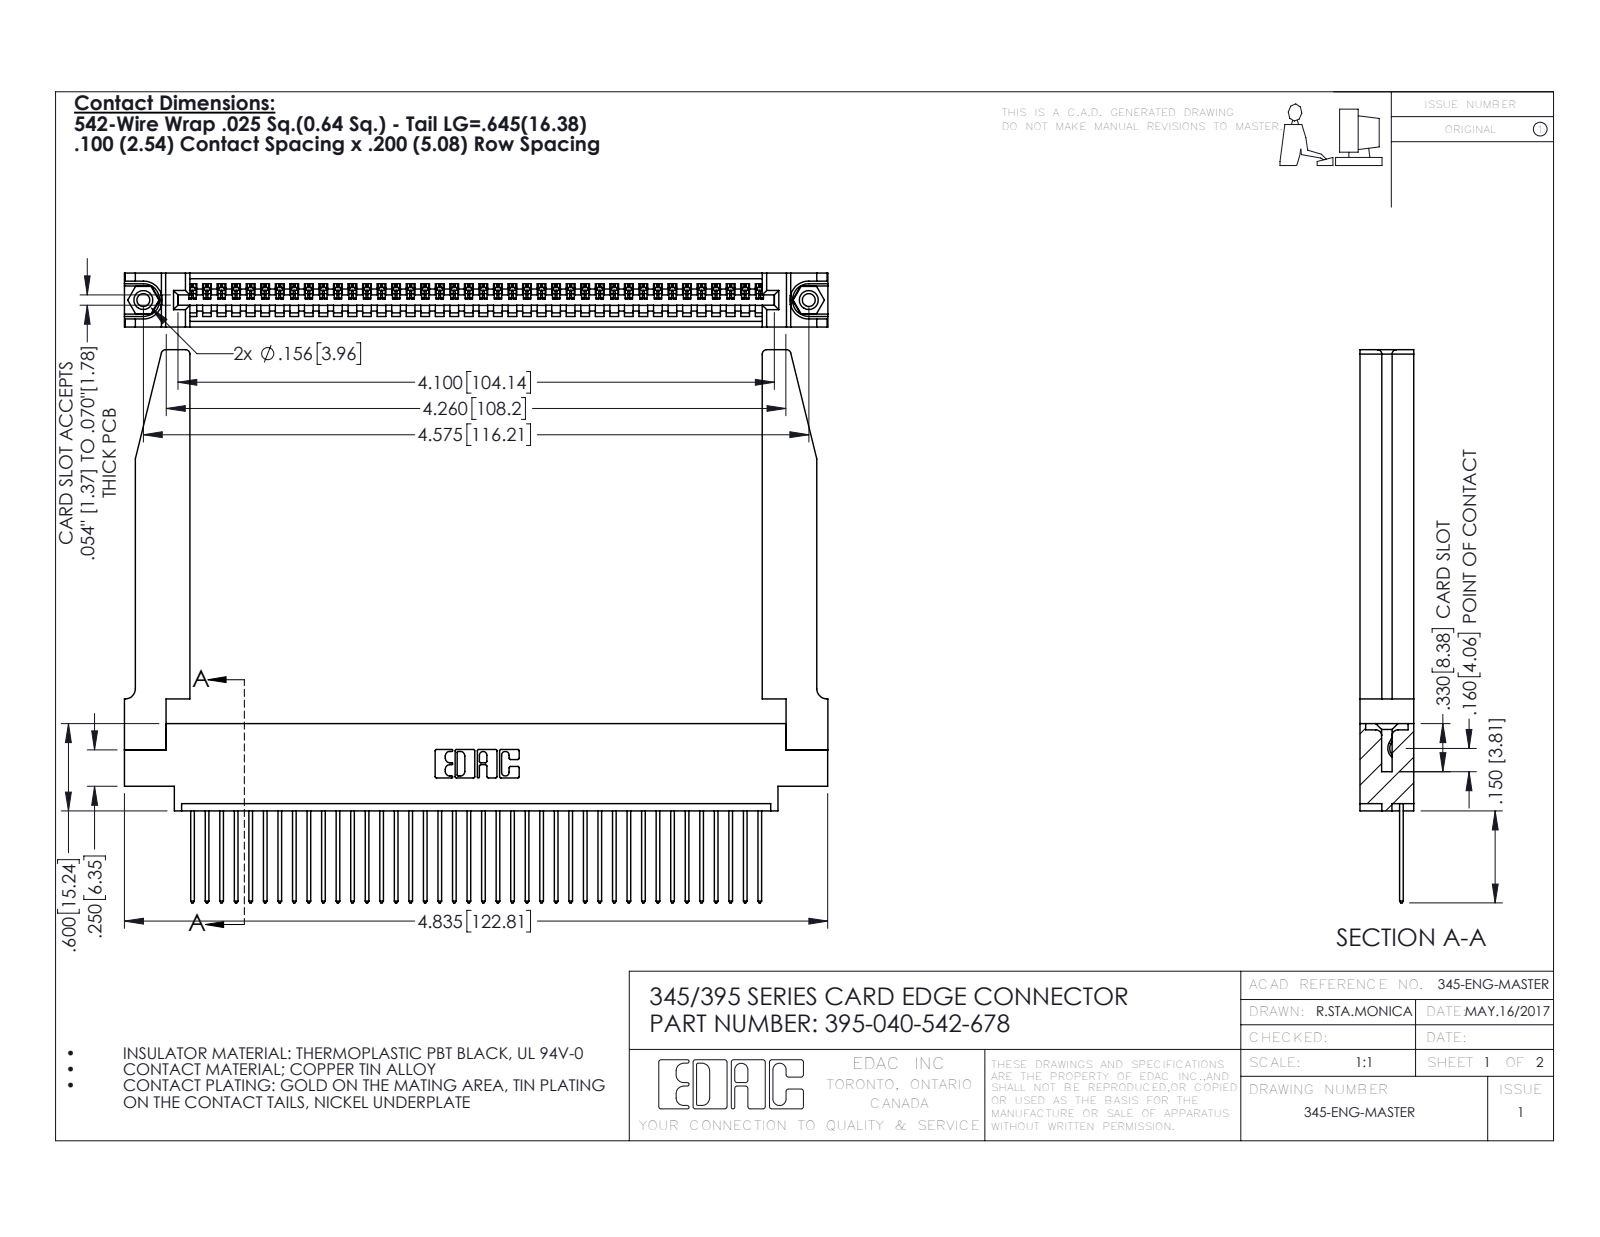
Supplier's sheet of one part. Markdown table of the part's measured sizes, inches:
| quantity | value |
| --- | --- |
| part name | 345-250-001_345-250-001-102; 345-220-078_345-220-078; 345 Part_0.170 Offset - 0.156 Dia-TH; 345-292-001_345-293-142 (+1 more) |
| STEP written by | SolidWorks 2016 (CONFIG_CONTROL_DESIGN) |
| units | inches |
| bodies | 45 solids, 2684 faces (1826 planar, 806 cylindrical, 52 other) |
| overall size | 4.836 × 3.802 × 0.37 |
| volume | 1.184 in³ |
| surface area | 35.58 in² |
| round holes (diameter × count) | 0.089 × 2, 0.125 × 2, 0.156 × 2, 0.064 × 1 |
| round bosses / shafts (diameter × count) | 0.155 × 2 |
| partial cylindrical surfaces (radius × count) | 0.006 × 80, 0.01 × 80, 0.01 × 22, 0.03 × 8, 0.007 × 6, 0.031 × 6, 0.026 × 3, 0.031 × 2 |
| main face-to-face distances | 0.37, 0.072, 0.298, 0.098, 0.272, 0.025, 0.2, 0.225, 0.148, 0.15 |
| hole center spacings | 0.27, 4.339, 4.575 |
